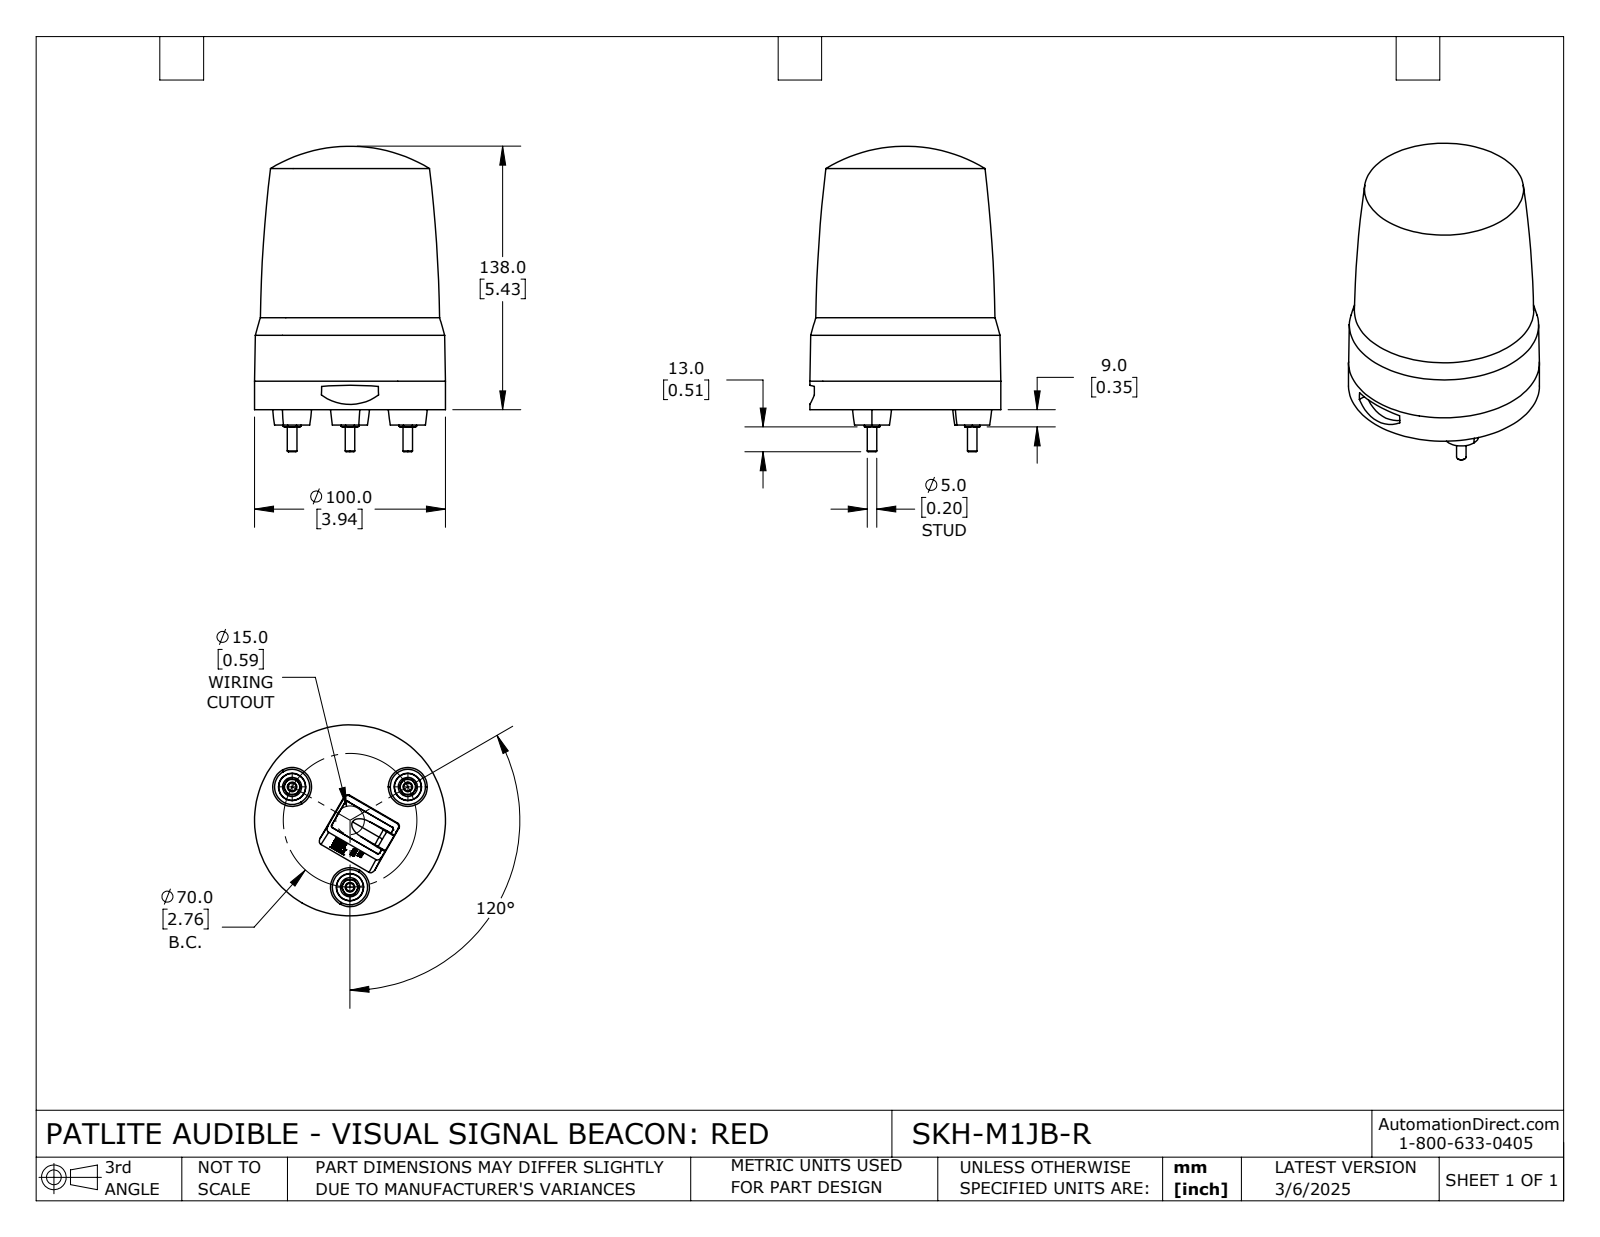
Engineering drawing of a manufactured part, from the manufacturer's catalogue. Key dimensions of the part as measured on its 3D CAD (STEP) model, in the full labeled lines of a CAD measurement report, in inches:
Part name (STEP PRODUCT): SKH-M1JB-R
STEP written by: SolidWorks 2024 (CONFIG_CONTROL_DESIGN)
Units: inches
Bodies: 1 solid, 446 faces (211 planar, 22 cylindrical, 213 other)
Overall size (bounding box): 6.299 × 3.937 × 3.937
Volume: 54.94 in³ · Surface area: 85.92 in²
Round bosses / shafts (diameter × count): ⌀0.394 ×3, ⌀0.197 ×3, ⌀3.937 ×1
Partial cylindrical surfaces — rounded edges, fillets, slot ends (radius × count): R0.079 ×4, R0.199 ×2, R1.772 ×1, R3.154 ×1
Main face-to-face distances: 0.315, 0.585, 0.27, 0.063, 0.648, 0.333, 0.15, 0.165, 0.435, 0.498
